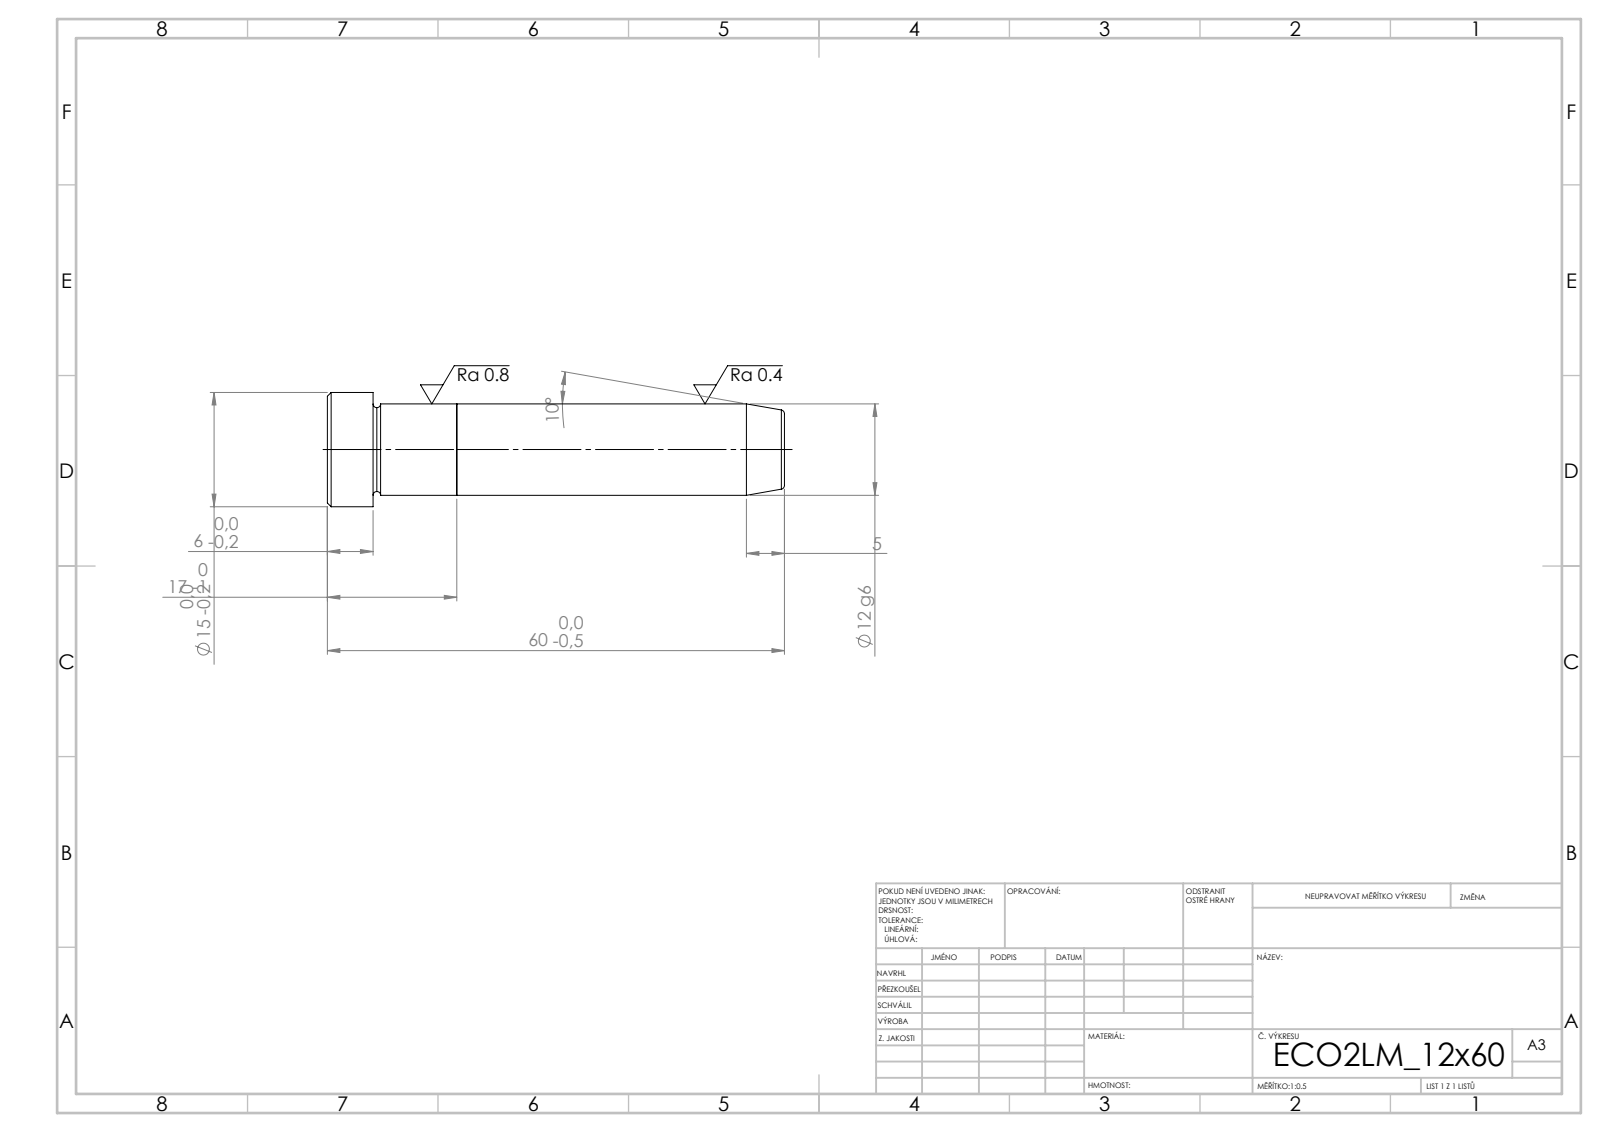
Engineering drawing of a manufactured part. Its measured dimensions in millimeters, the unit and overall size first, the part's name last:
Units: millimetres
Overall size (bounding box): 60 × 15 × 15
Round bosses / shafts (diameter × count): ⌀15 ×1, ⌀12 ×1
Main face-to-face distances: 17, 43, 60, 54, 11, 6
Volume: 7 067 mm³ · Surface area: 2 856 mm²
Bodies: 2 solids, 21 faces (5 planar, 6 cylindrical, 10 other)
STEP written by: SolidWorks 2019 (CONFIG_CONTROL_DESIGN)
